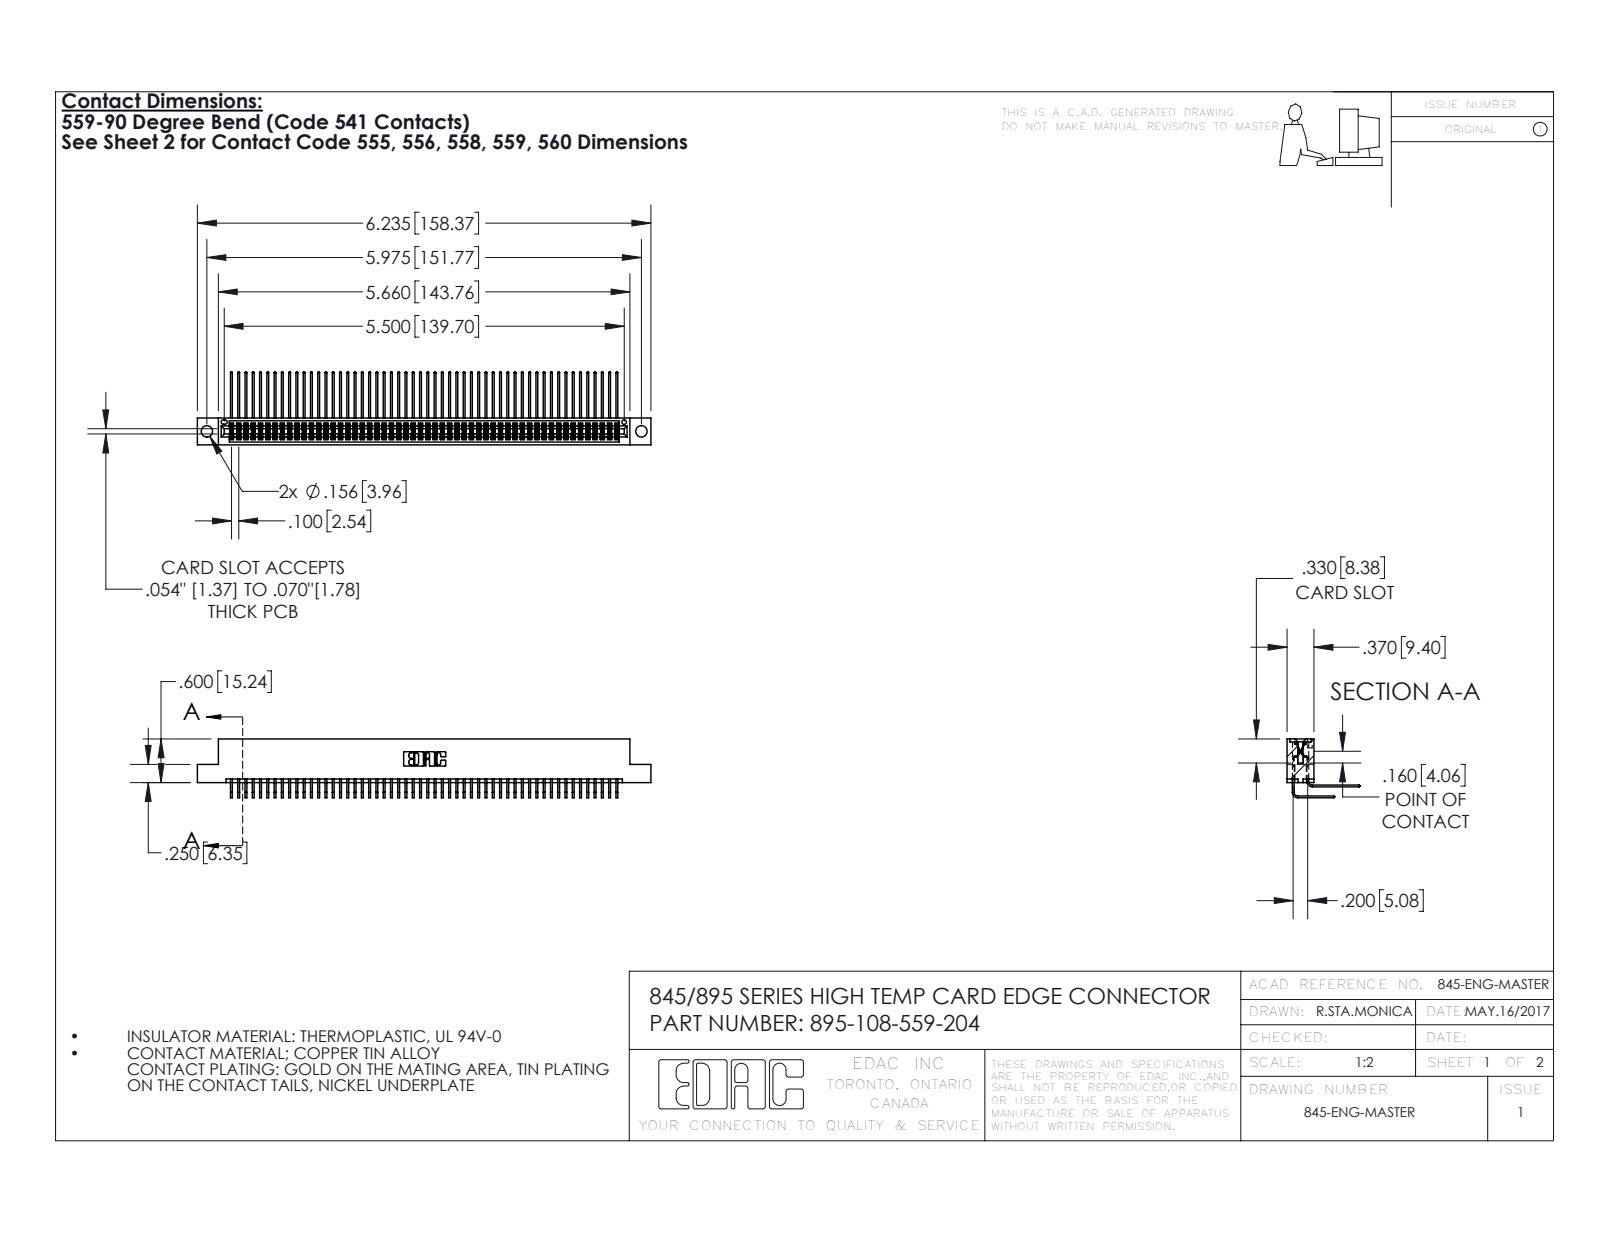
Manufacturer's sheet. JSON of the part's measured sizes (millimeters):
{"part_name": "345 Part_Flush Mounting Lugs - 0.156 Dia-TH; 345-292-001_558 559 Tail - 1; 345-292-001_559 Tail - 2; 395-108-559-204", "step_written_by": "SolidWorks 2016 (CONFIG_CONTROL_DESIGN)", "units": "millimeters", "bodies": {"solids": 109, "faces": 5742, "planar": 3860, "cylindrical": 1882, "other": 0}, "overall_size": [158.4, 25.5, 20.5], "volume_mm3": 16000, "surface_area_mm2": 26670, "round_holes": [[4, 2], [1.6, 1]], "partial_cylinders_radius": [[0.2, 163], [0.3, 22], [0.2, 6], [0.8, 6], [0.7, 3], [0.4, 2], [0.5, 2], [0.6, 2]], "face_to_face_distances": [1.8, 7.6, 5.1, 9.4, 2.5, 6.9, 0.6, 5.7, 4.4, 3.8], "hole_center_spacings": [6.9, 145.8, 151.8]}
